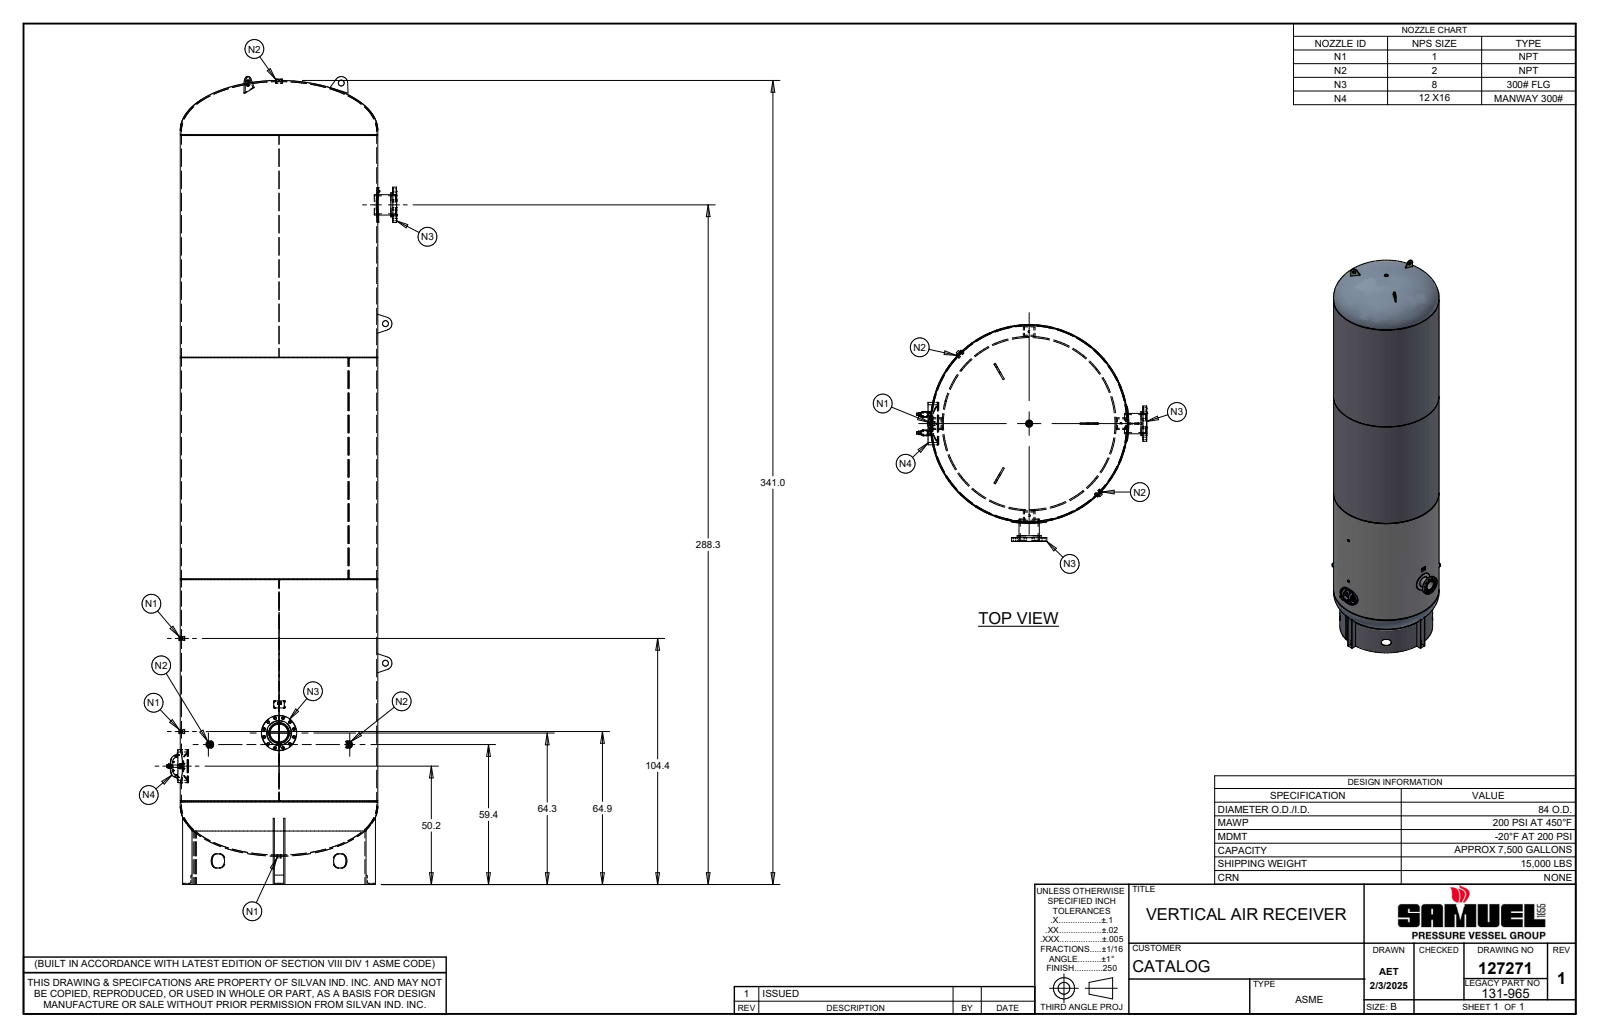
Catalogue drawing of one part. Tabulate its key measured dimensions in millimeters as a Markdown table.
| quantity | value |
| --- | --- |
| part name | 127271; 131-965SF-SL1; 131-965SF-SL2; 131-965SF-SL3 (+8 more) |
| STEP written by | Autodesk Inventor 2022 (AUTOMOTIVE_DESIGN) |
| units | millimeters |
| bodies | 60 solids, 1090 faces (542 planar, 219 cylindrical, 329 other) |
| overall size | 8703.2 × 2484.4 × 2336.8 |
| volume | 803 900 000 mm³ |
| surface area | 127 700 000 mm² |
| round holes (diameter × count) | 25.4 × 26, 63.5 × 5, 22.2 × 4, 30.3 × 3, 55.5 × 3, 56.7 × 3, 10.9 × 2, 22 × 2, 28.6 × 2, 50.8 × 2, 193.7 × 2, 203.2 × 2 |
| round bosses / shafts (diameter × count) | 76.2 × 3, 44.5 × 3, 381 × 2, 373 × 2, 269.9 × 2, 260.4 × 2, 25.4 × 2, 1879.6 × 1 |
| partial cylindrical surfaces (radius × count) | 12.7 × 12, 19.7 × 12, 9.5 × 10, 76.2 × 7, 25.4 × 6, 69.9 × 5, 19.1 × 4, 29.4 × 4 |
| main face-to-face distances | 12.7, 114.3, 101.6, 50.8, 127, 990.6, 63.5, 2387.6, 1041.4, 4781.6 |
| hole center spacings | 165.1, 85.5, 286, 233.5, 233.5, 318.9, 318.9, 165.1 |
